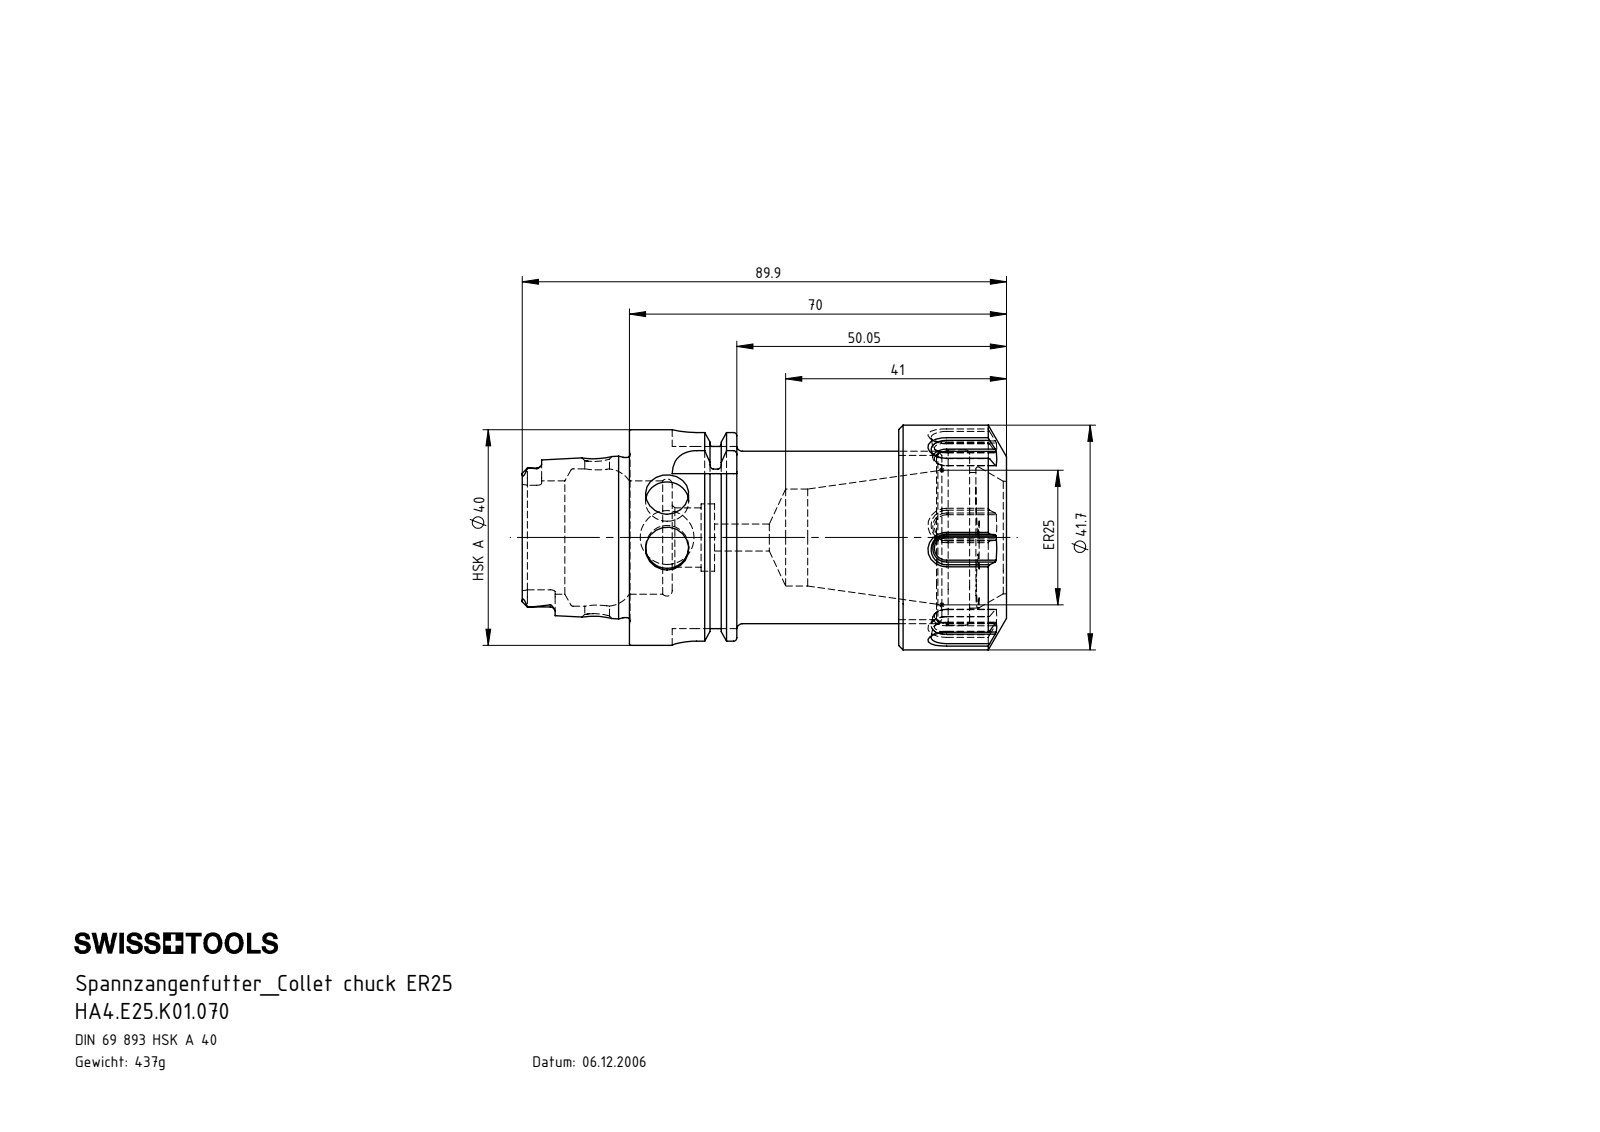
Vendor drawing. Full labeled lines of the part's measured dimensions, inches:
Part name (STEP PRODUCT): HA4-E25.K01.070_B_Fertigbearbeitung; HA4.E25.K01.070; E25-ER1.001.020
STEP written by: SolidWorks 2017 (CONFIG_CONTROL_DESIGN)
Units: inches
Bodies: 2 solids, 262 faces (98 planar, 63 cylindrical, 101 other)
Overall size (bounding box): 3.539 × 1.642 × 1.642
Volume: 3.398 in³ · Surface area: 33.4 in²
Round holes (diameter × count): ⌀0.315 ×2, ⌀0.181 ×1, ⌀0.197 ×1, ⌀0.394 ×1, ⌀0.433 ×1, ⌀0.492 ×1, ⌀0.709 ×1, ⌀0.823 ×1, ⌀0.827 ×1, ⌀1.004 ×1, ⌀1.201 ×1, ⌀1.28 ×1
Round bosses / shafts (diameter × count): ⌀1.642 ×1, ⌀1.575 ×1, ⌀1.368 ×1, ⌀1.26 ×1, ⌀1.17 ×1
Partial cylindrical surfaces — rounded edges, fillets, slot ends (radius × count): R0.035 ×6, R0.074 ×4, R0.177 ×4, R0.479 ×2
Main face-to-face distances: 1.969, 1.97, 0.472, 2.756, 0.787, 2.486, 0.518, 0.27, 0.785, 1.183
